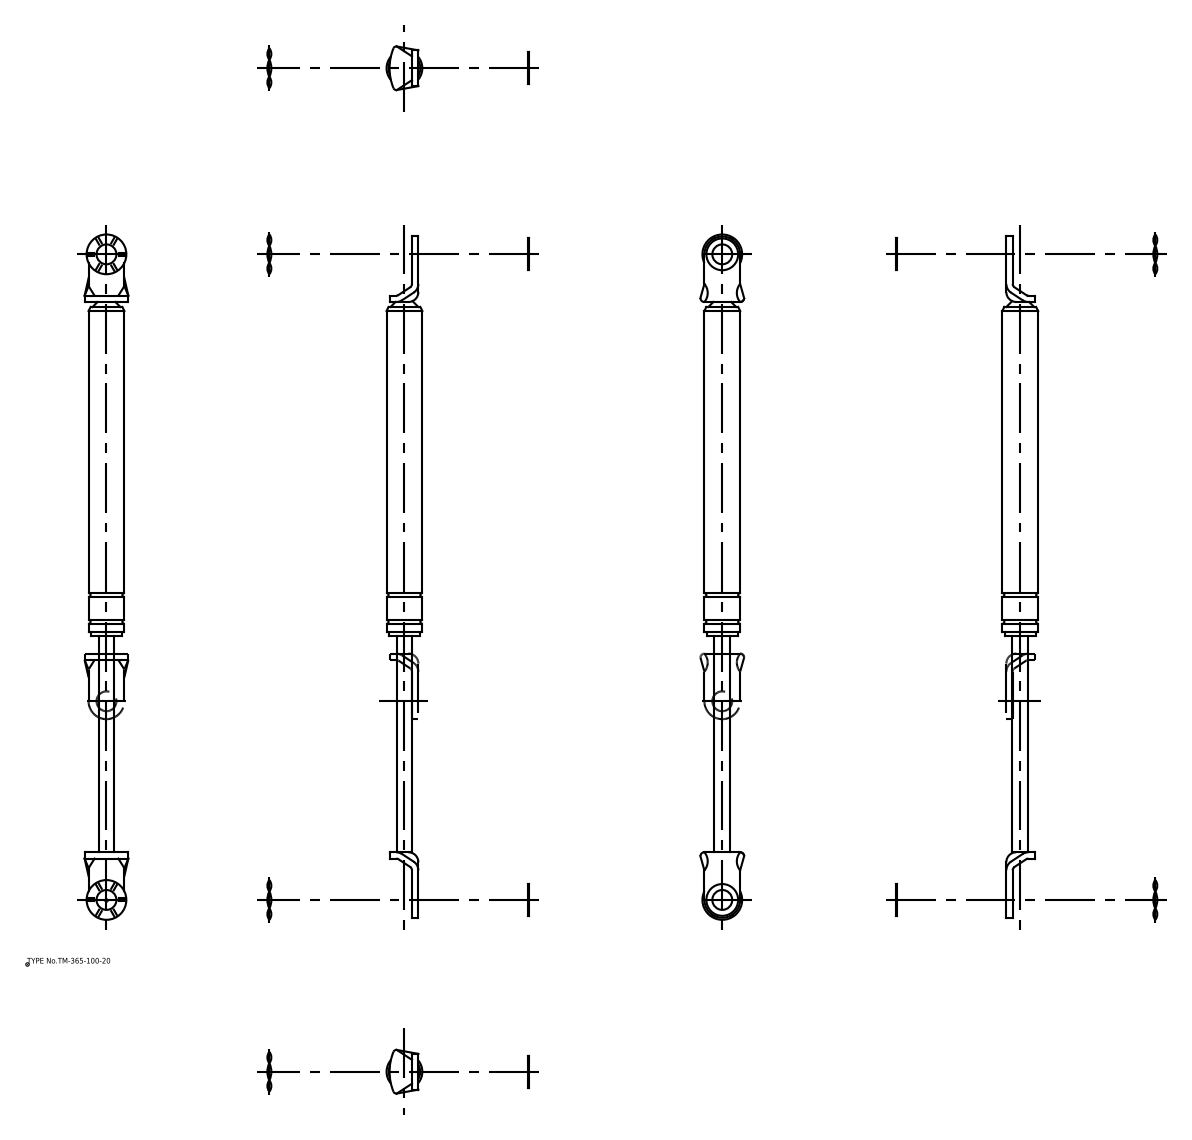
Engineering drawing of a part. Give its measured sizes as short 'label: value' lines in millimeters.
name: ウェーブワッシャー; ワッシャー; 本体; 本体_div
written by: spGate 16.7.1 (AUTOMOTIVE_DESIGN)
unit: mm
bodies: 6 solids, 94 faces (42 planar, 44 cylindrical, 8 other)
size: 345 × 22 × 18.5
volume: 53 207 mm³; area: 18 252 mm²
holes: 2× ⌀10
bosses: 3× ⌀16, 2× ⌀20, 1× ⌀18.5, 1× ⌀18, 1× ⌀8
rounds: 2× R4.4, 2× R5, 2× R9, 1× R26.32
face distances: 3.2, 2, 5.2, 280.2, 3.7, 5.7, 0.5, 171.2, 112.2, 283.4
hole spacings: 325
